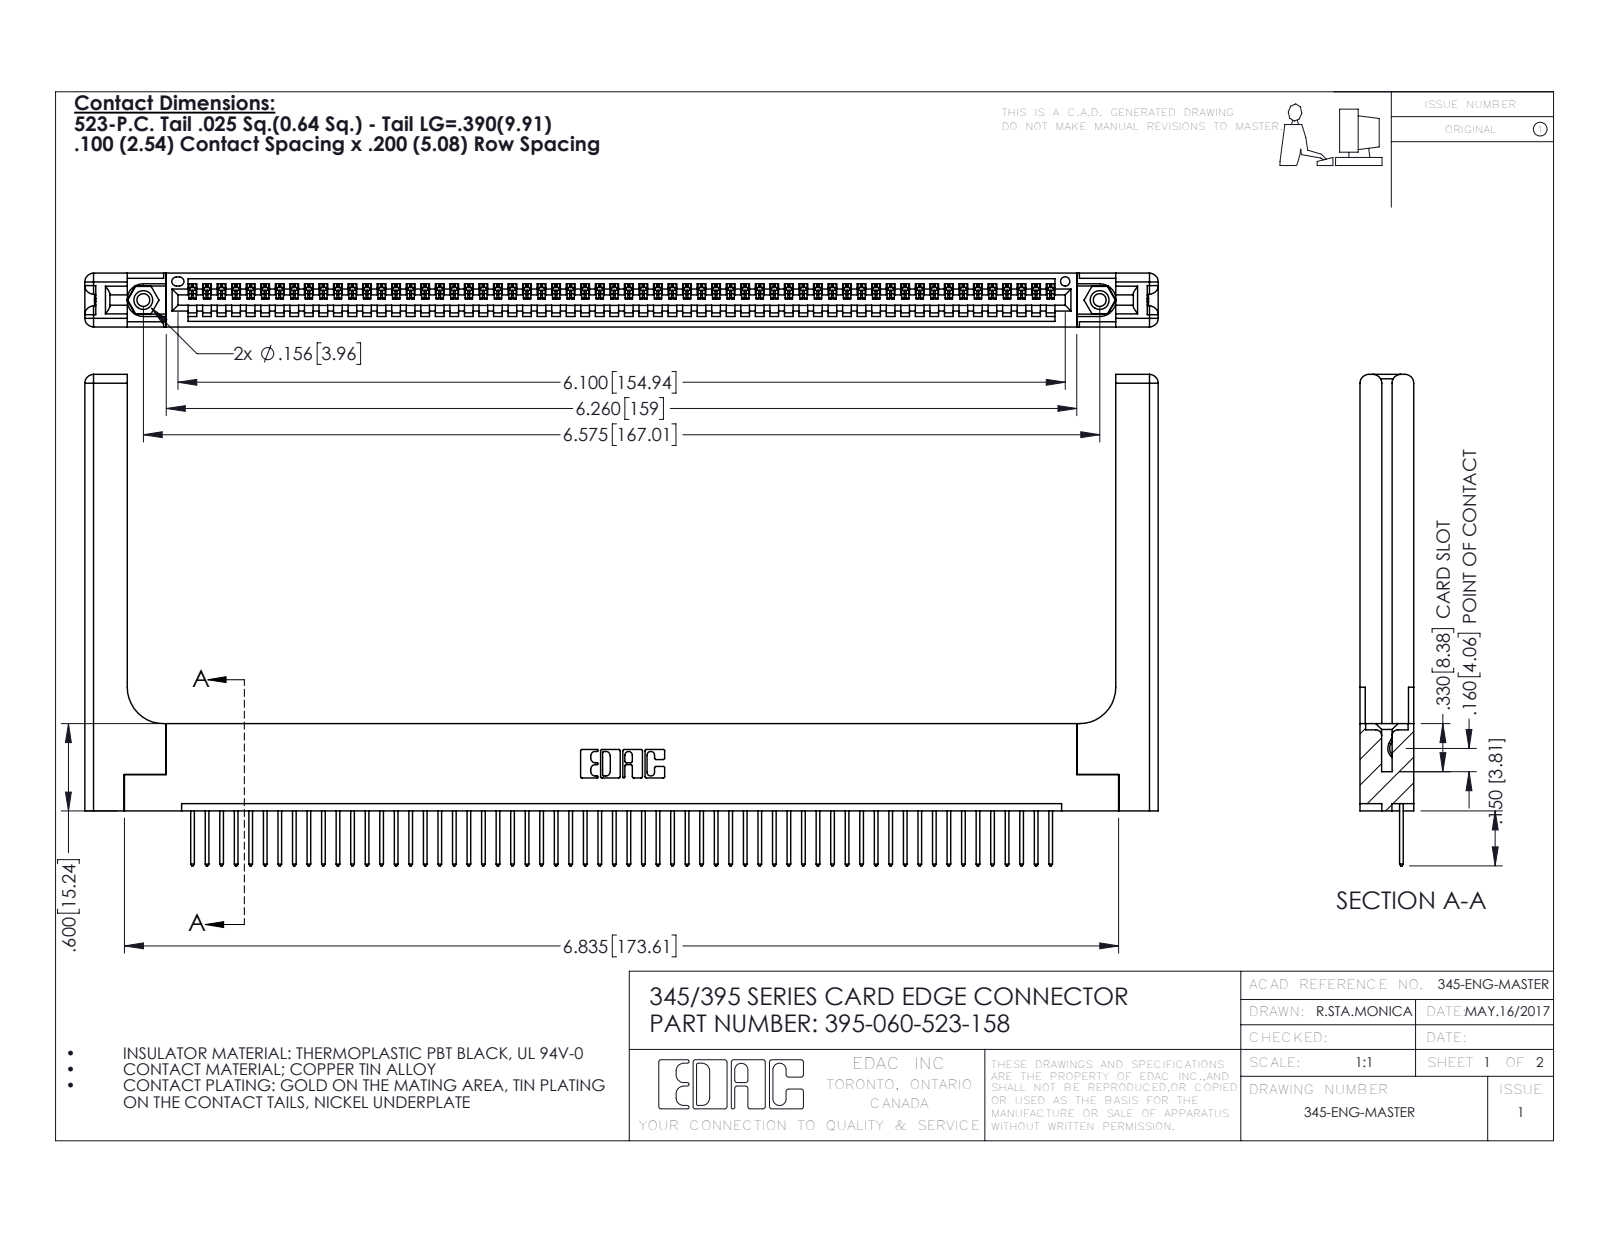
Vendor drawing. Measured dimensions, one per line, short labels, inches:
name: 395-060-523-158; 345-250-001_345-250-001-102; 345 Part_Flush Mounting Lugs - 0.156 Dia-TH; 345-220-058_345-220-058 (+1 more)
written by: SolidWorks 2016 (CONFIG_CONTROL_DESIGN)
unit: in
bodies: 65 solids, 3862 faces (2628 planar, 1174 cylindrical, 60 other)
size: 7.379 × 3.377 × 0.37
volume: 1.613 in³; area: 45.63 in²
holes: 2× ⌀0.089, 2× ⌀0.125, 2× ⌀0.156, 1× ⌀0.064
bosses: 2× ⌀0.155
rounds: 120× R0.006, 120× R0.01, 22× R0.01, 16× R0.06, 6× R0.007, 6× R0.031, 3× R0.026, 2× R0.03
face distances: 0.072, 0.298, 0.37, 0.2, 0.098, 0.272, 0.025, 0.225, 0.148, 0.15
hole spacings: 0.27, 6.339, 6.575
